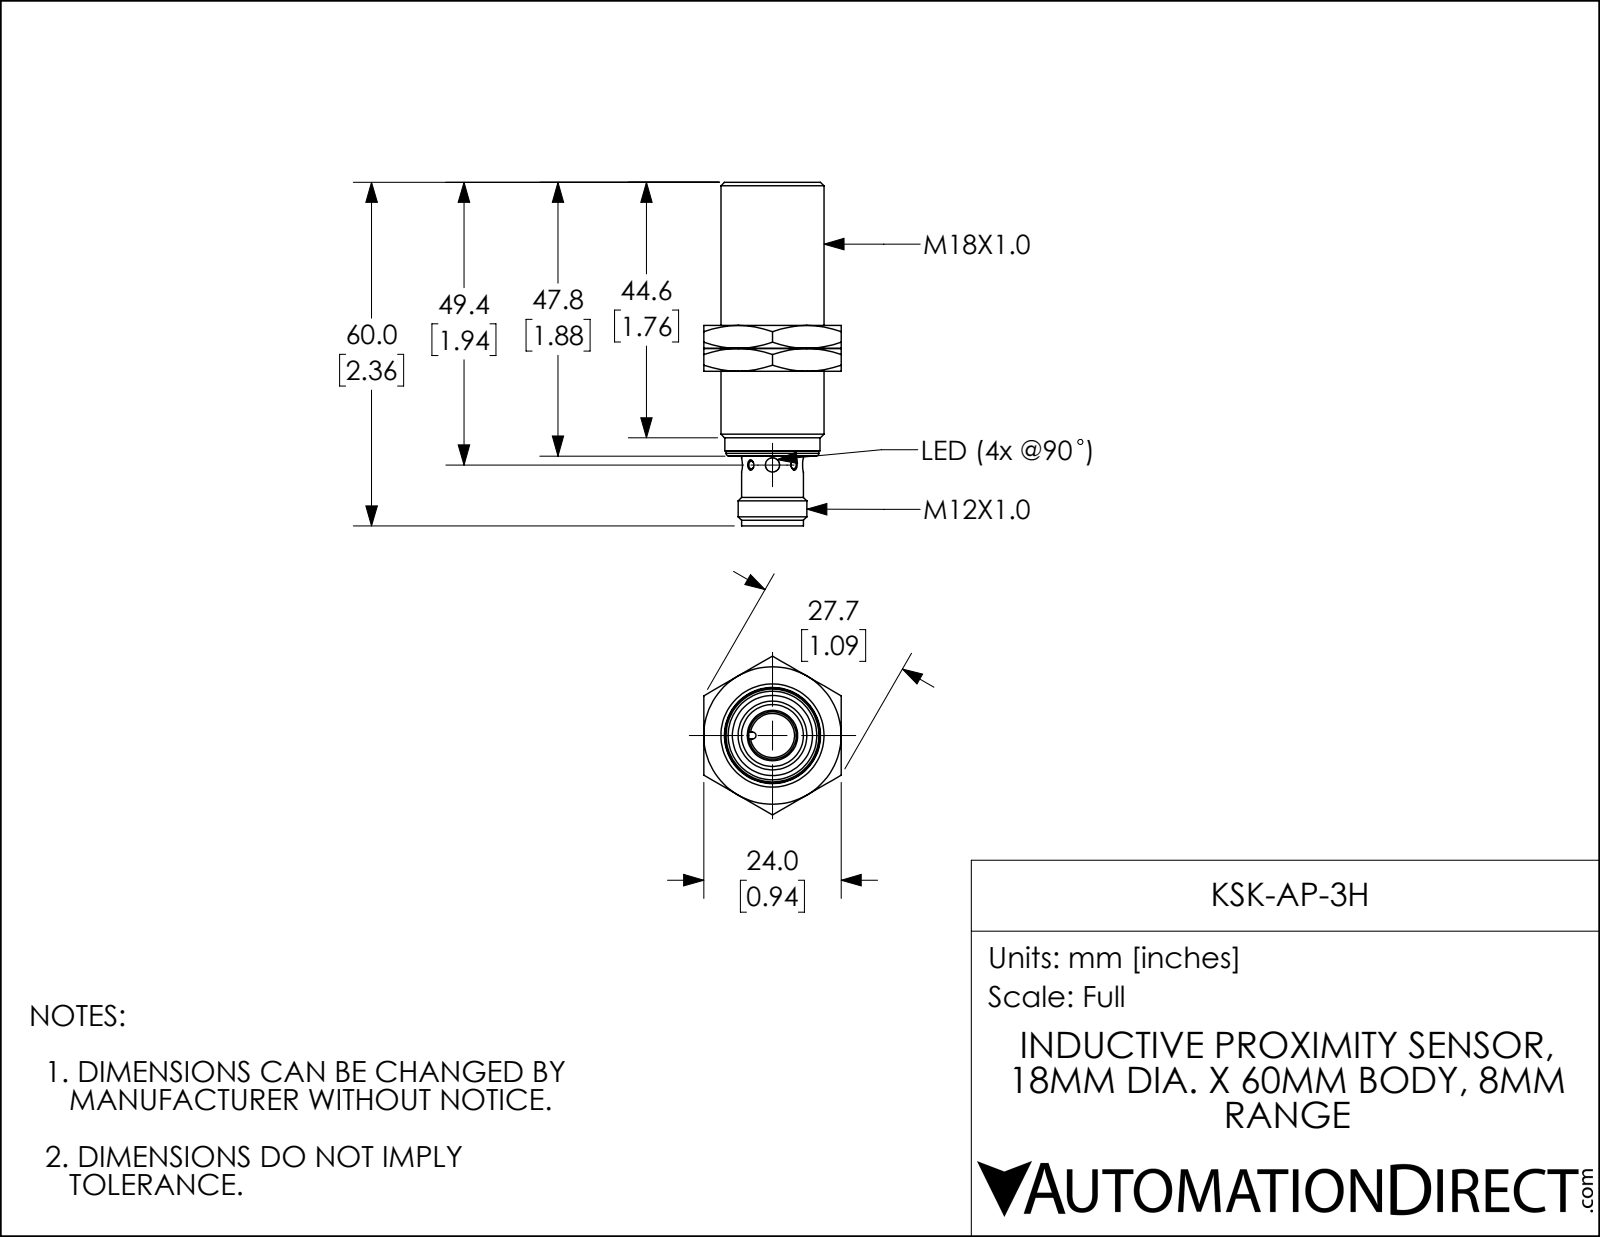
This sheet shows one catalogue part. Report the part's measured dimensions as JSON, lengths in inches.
{"part_name": "KSK-AP-3H", "step_written_by": "SolidWorks 2017 (AUTOMOTIVE_DESIGN)", "units": "inches", "bodies": {"solids": 3, "faces": 94, "planar": 28, "cylindrical": 16, "other": 50}, "overall_size": [2.362, 1.091, 0.945], "volume_in3": 0.904, "surface_area_in2": 9.234, "round_holes": [[0.327, 1], [0.634, 1], [0.666, 1]], "round_bosses_or_shafts": [[0.709, 1], [0.654, 1], [0.638, 1], [0.63, 1], [0.472, 1], [0.425, 1]], "partial_cylinders_radius": [[0.213, 4], [0.024, 1]], "face_to_face_distances": [0.157, 0.945, 1.142, 1.299, 0.315, 0.984, 0.583, 0.74, 0.898, 1.882]}
